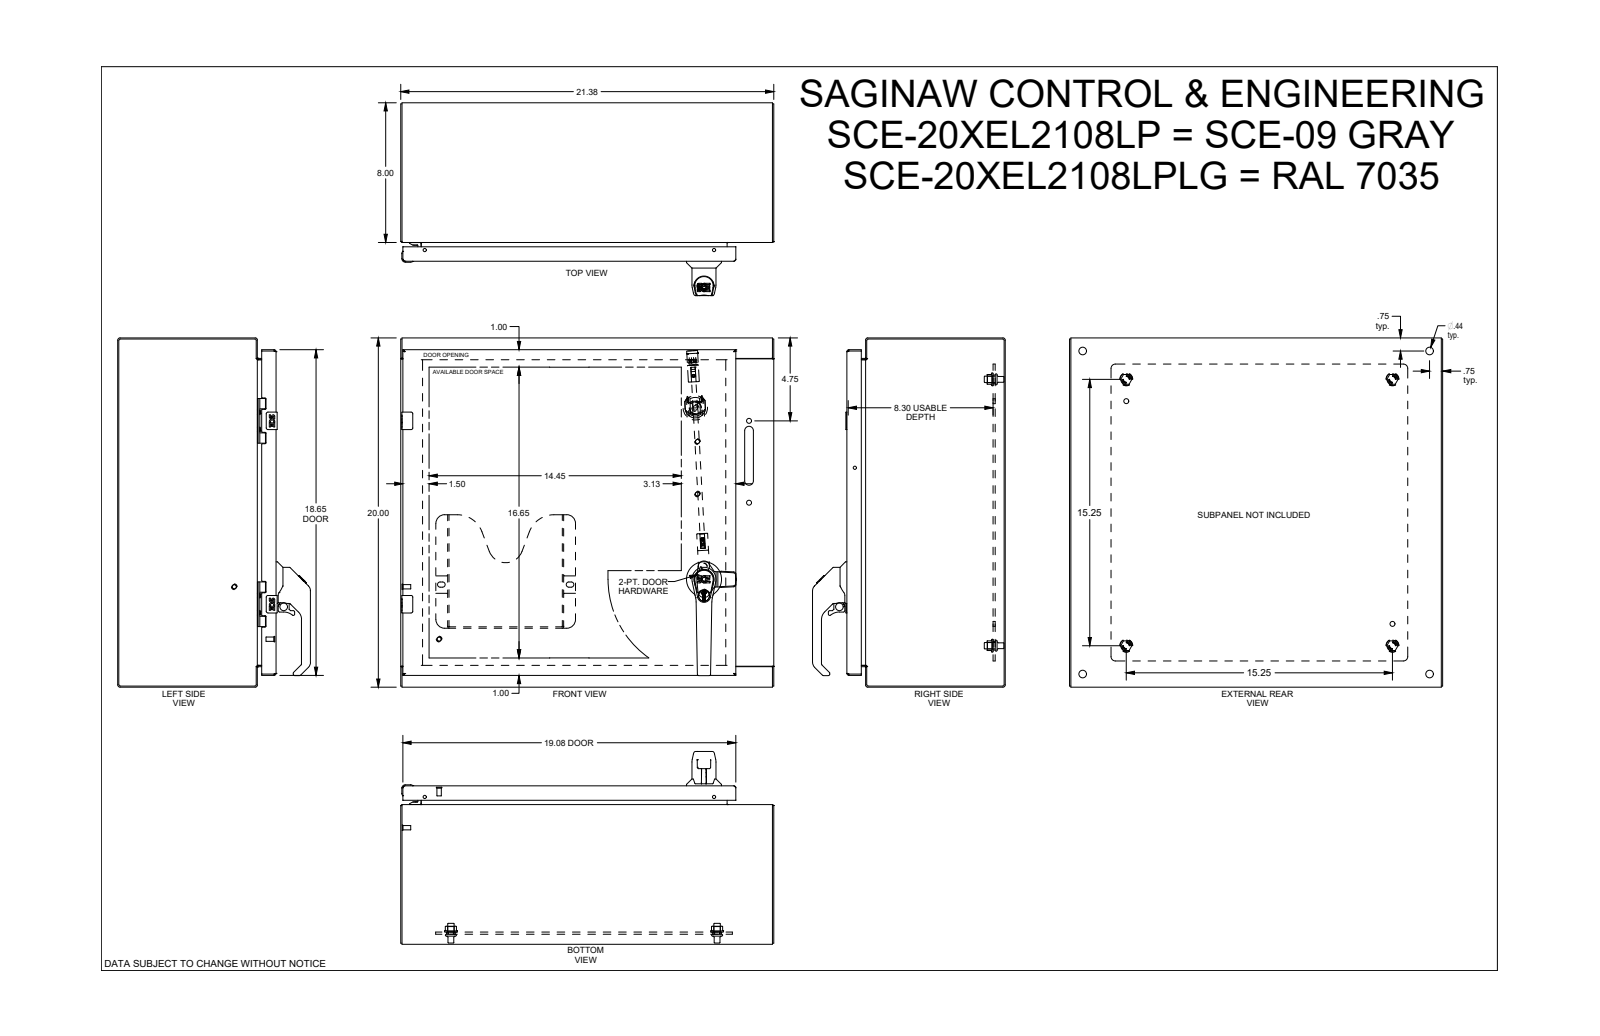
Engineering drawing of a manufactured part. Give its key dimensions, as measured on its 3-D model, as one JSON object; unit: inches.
{"part_name": "SCE-20XEL2108LP", "step_written_by": "SolidWorks 2021 (AUTOMOTIVE_DESIGN)", "units": "inches", "bodies": {"solids": 55, "faces": 3180, "planar": 1287, "cylindrical": 953, "other": 940}, "overall_size": [21.375, 20, 11.036], "volume_in3": 189.4, "surface_area_in2": 4363, "round_holes": [[0.172, 4], [0.205, 4], [0.244, 4], [0.281, 4], [0.367, 4], [0.375, 4], [0.437, 4], [0.5, 4], [0.04, 2], [0.127, 2], [0.138, 2], [0.156, 2]], "round_bosses_or_shafts": [[0.248, 7], [0.17, 6], [0.33, 4], [0.25, 4], [0.24, 4], [0.196, 3], [0.375, 2], [0.375, 2]], "partial_cylinders_radius": [[0.03, 62], [0.015, 44], [0.02, 35], [0.02, 34], [0.039, 28], [0.01, 26], [0.04, 25], [0.079, 23]], "face_to_face_distances": [0.075, 8.993, 9.068, 8.918, 19.925, 21.3, 0.7, 0.625, 0.5, 0.125], "hole_center_spacings": [10.5, 15.25, 19.052, 19.875, 0.472, 0.493, 0.494, 0.724]}
